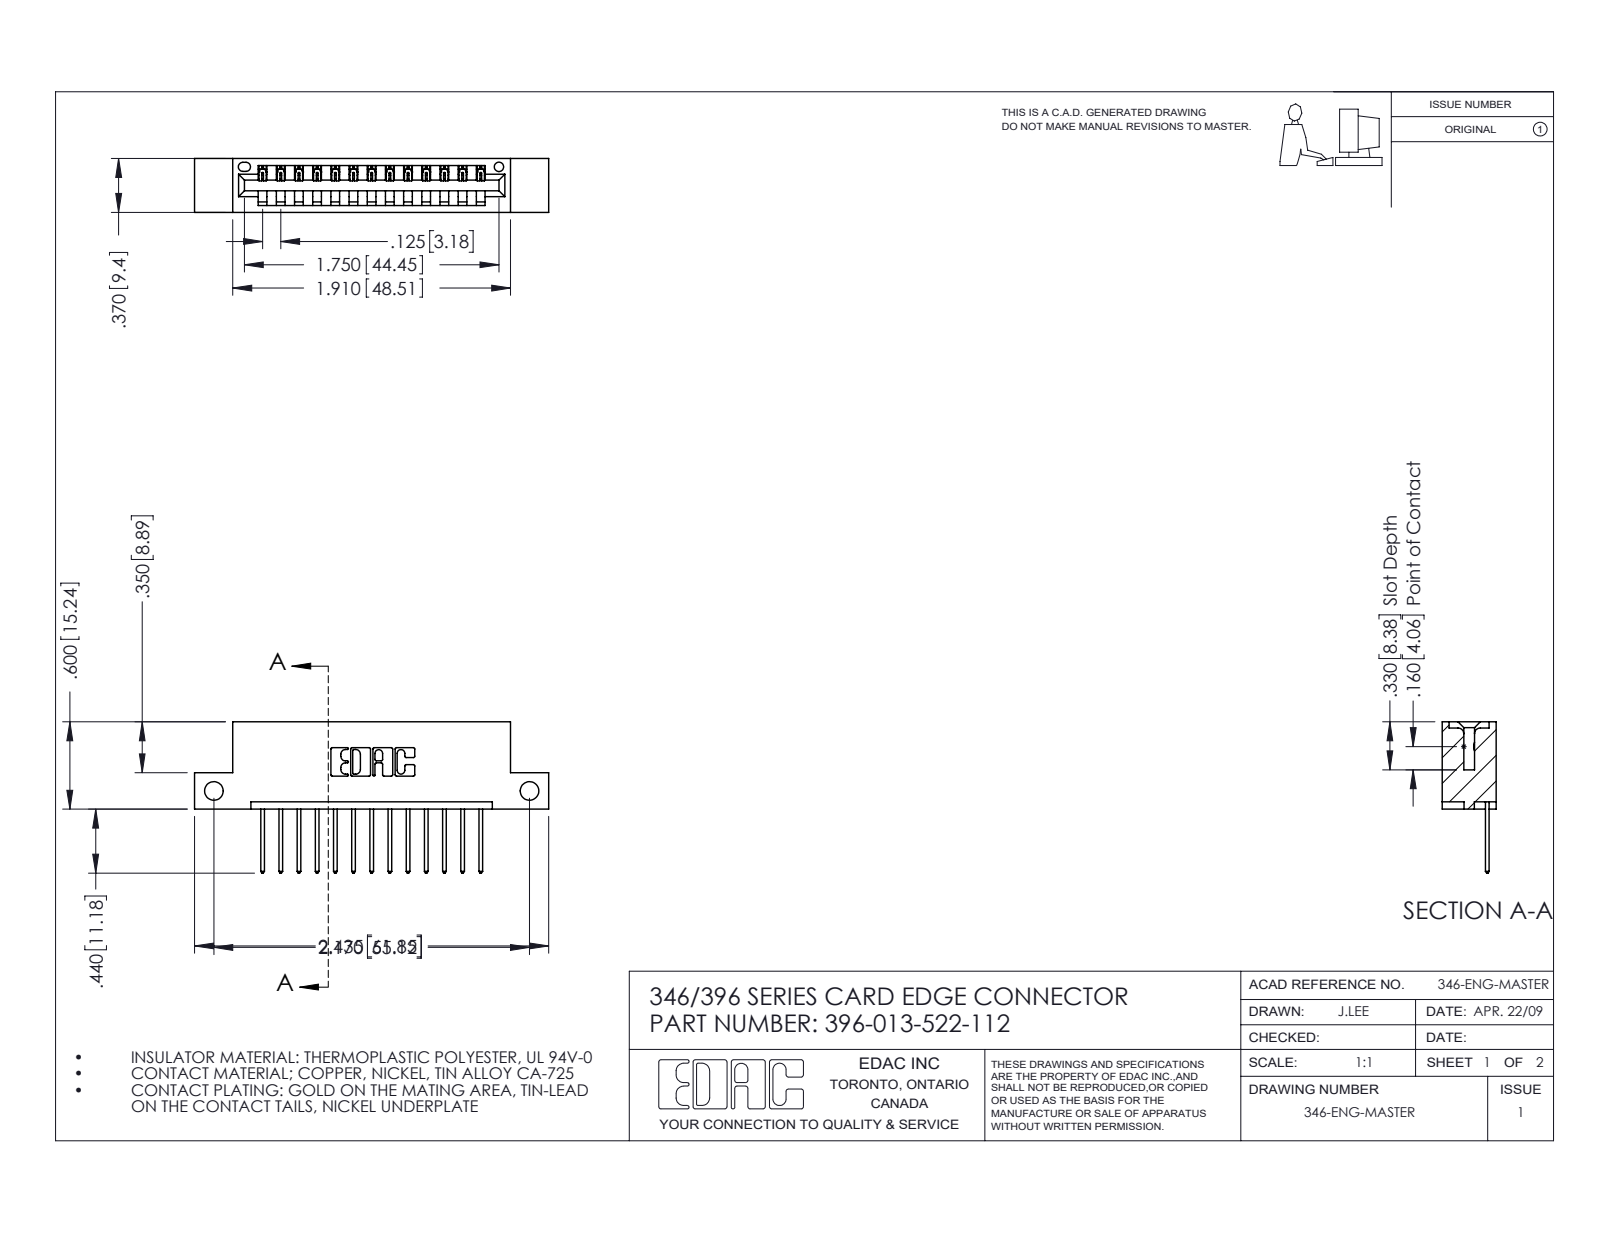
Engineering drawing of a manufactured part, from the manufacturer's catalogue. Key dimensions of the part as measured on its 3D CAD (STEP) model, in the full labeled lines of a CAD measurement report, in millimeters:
Part name (STEP PRODUCT): 346 Part_Flush Mounting Lugs - Side Mount; 396-013-522-112; 345-292-001_345-293-122
STEP written by: SolidWorks 2016 (CONFIG_CONTROL_DESIGN)
Units: millimetres
Bodies: 14 solids, 876 faces (596 planar, 280 cylindrical, 0 other)
Overall size (bounding box): 61.8 × 26.4 × 9.4
Volume: 5 640 mm³ · Surface area: 6 632 mm²
Round holes (diameter × count): ⌀3.3 ×2, ⌀1.6 ×1
Partial cylindrical surfaces — rounded edges, fillets, slot ends (radius × count): R0.2 ×26, R0.3 ×26, R0.3 ×22, R0.2 ×6, R0.8 ×6, R0.7 ×3, R0.8 ×2, R1 ×2
Main face-to-face distances: 6.4, 1.2, 8.2, 9.4, 1.8, 7.6, 0.6, 3.8, 5.6, 2.5
Hole centre spacings: 55.1
